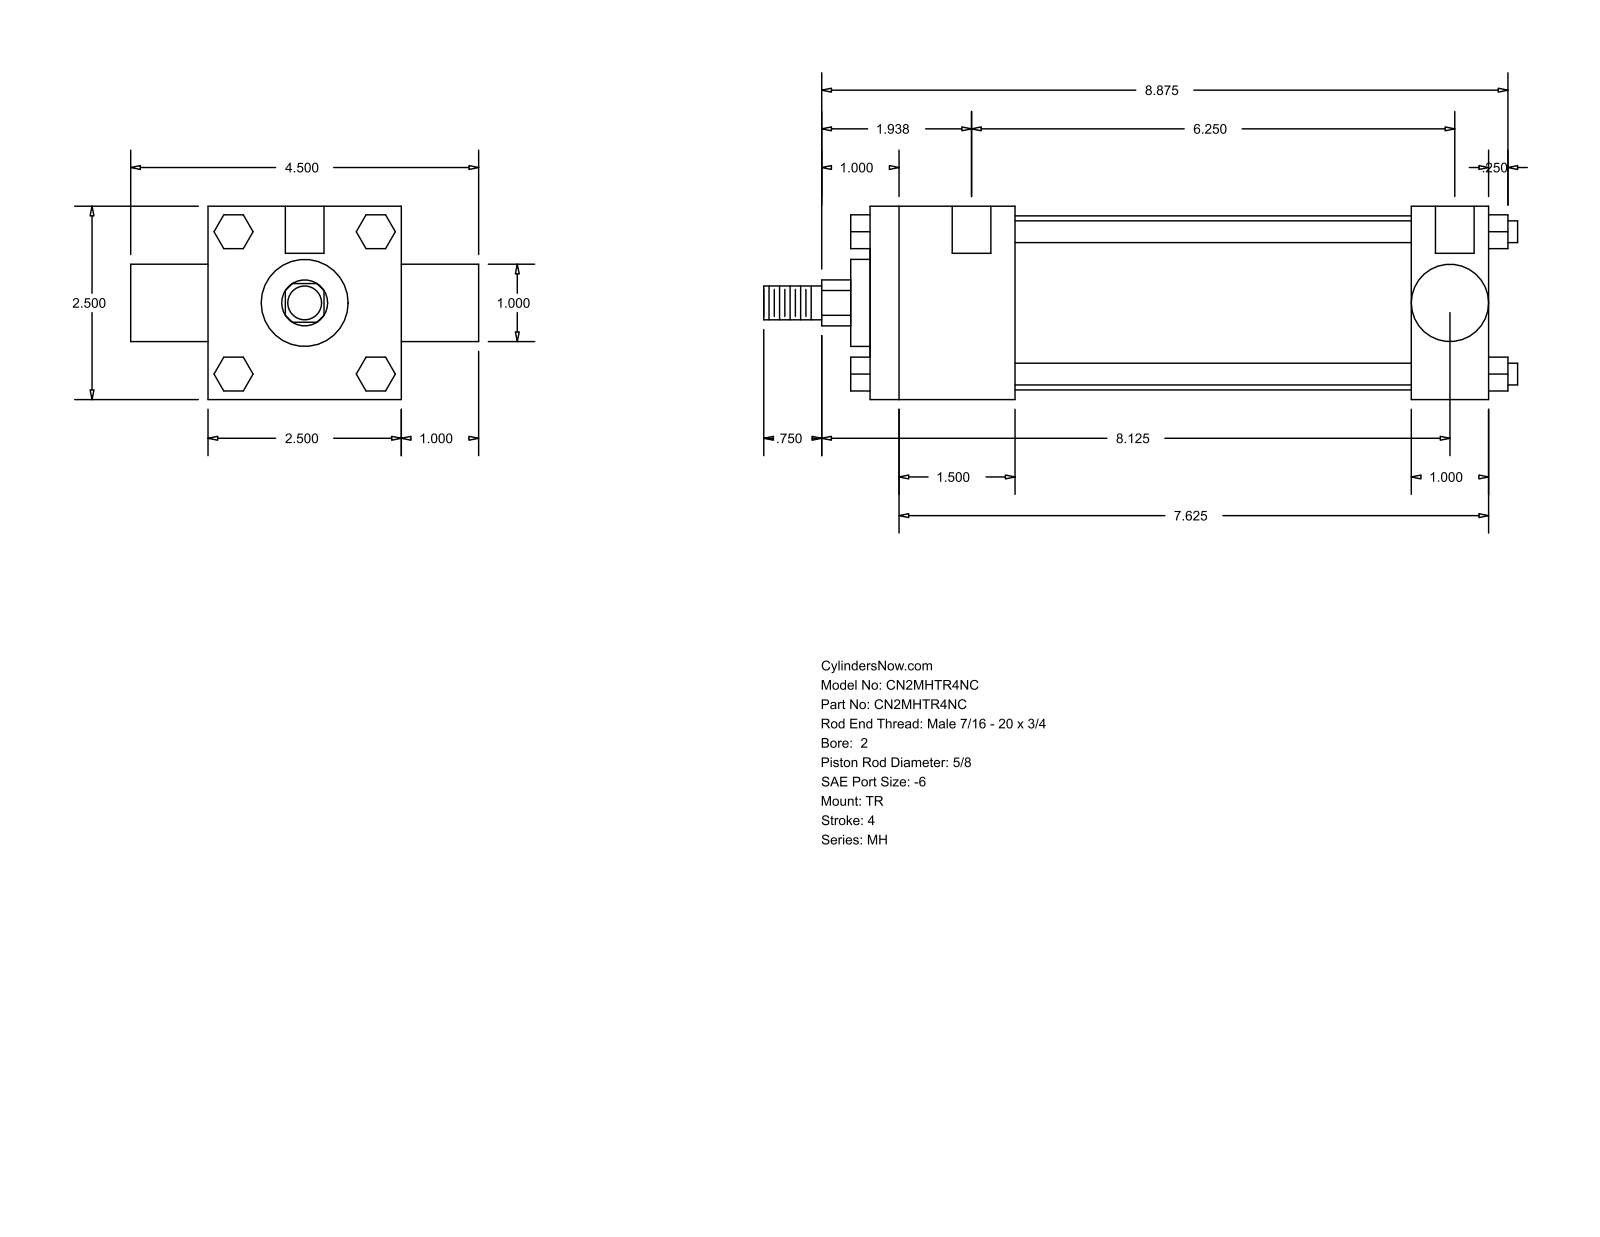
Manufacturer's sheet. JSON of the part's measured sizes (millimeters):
{"part_name": "MH_TR__0200_0.625", "step_written_by": "GSSL Pune (CONFIG_CONTROL_DESIGN)", "units": "millimeters", "bodies": {"solids": 0, "faces": 120, "planar": 92, "cylindrical": 28, "other": 0}, "overall_size": [247.65, 114.3, 63.5], "round_holes": [[5.56, 3], [12.7, 2]], "round_bosses_or_shafts": [[7.14, 4], [57.15, 1], [28.57, 1], [25.35, 1], [15.88, 1], [11.11, 1]], "partial_cylinders_radius": [[7.54, 1]], "face_to_face_distances": [63.5, 203.19, 47.62, 177.8, 130.18, 155.57, 25.39, 25.4, 88.9, 6.35], "hole_center_spacings": [3.18, 4.76, 158.75, 161.93, 163.51, 166.69]}
